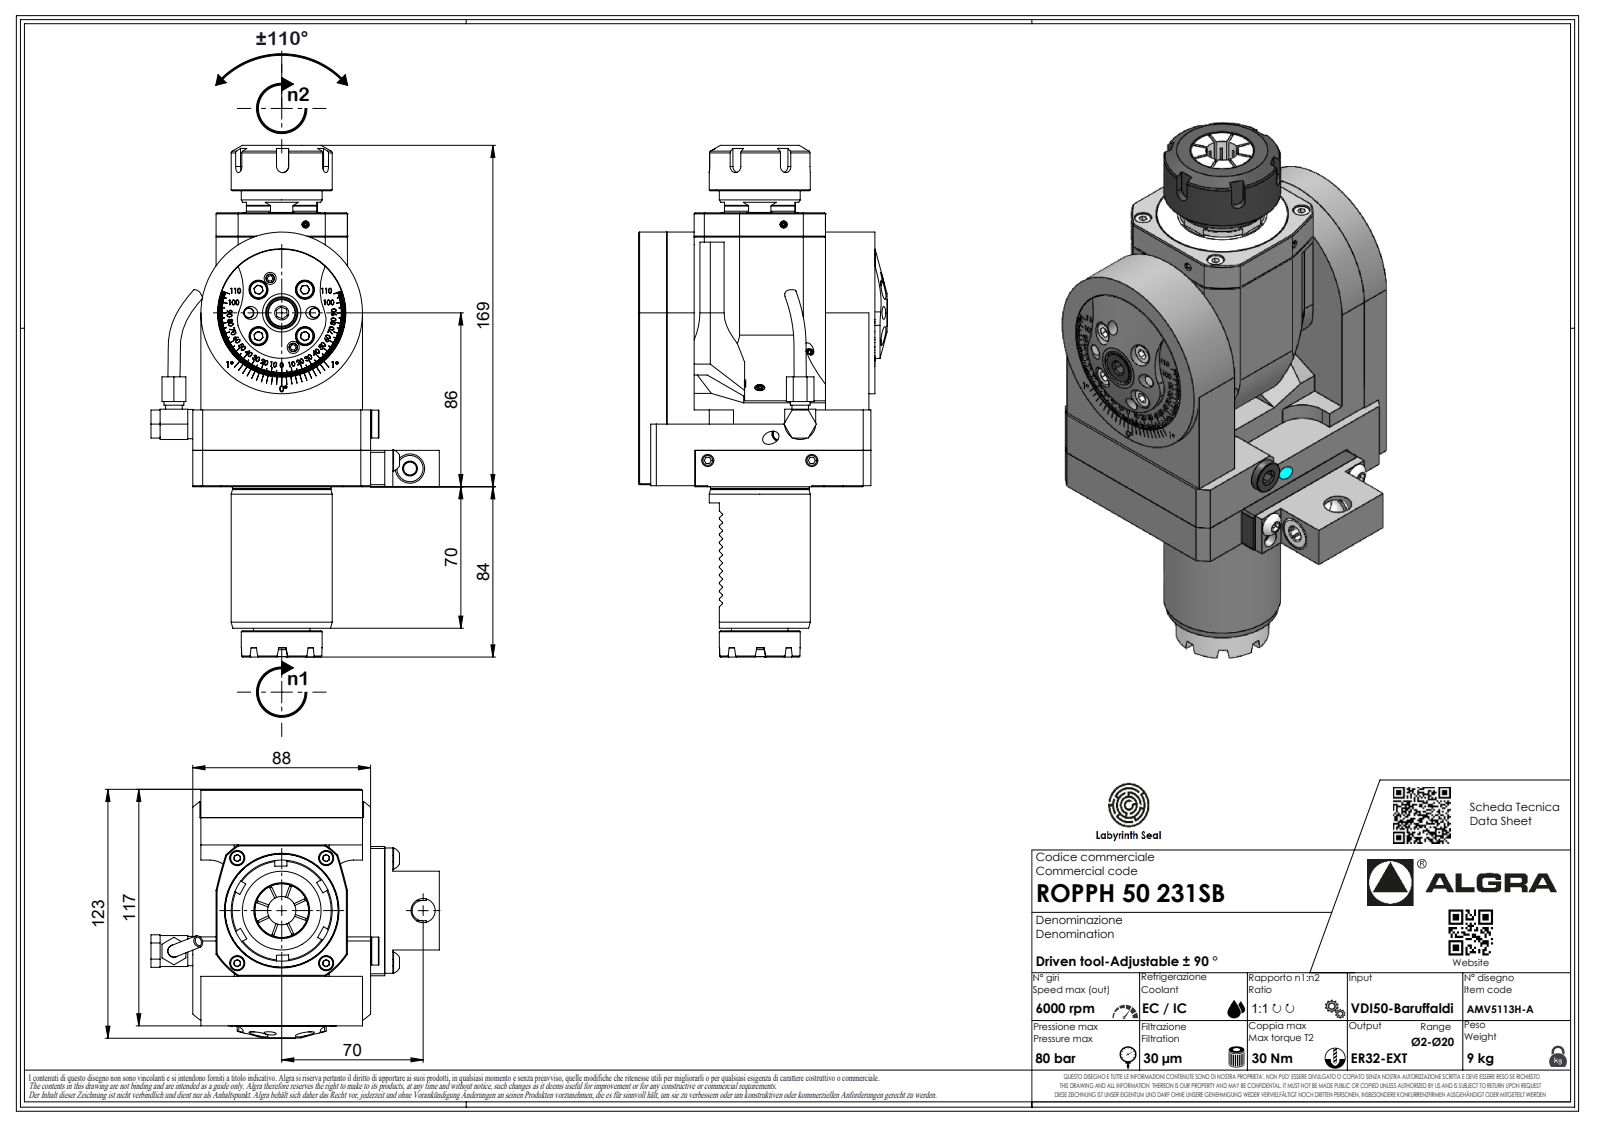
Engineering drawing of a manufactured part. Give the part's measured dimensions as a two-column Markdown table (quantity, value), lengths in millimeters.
| quantity | value |
| --- | --- |
| part name | ROPPH50231SB |
| STEP written by | SolidWorks 2023 (AUTOMOTIVE_DESIGN) |
| units | millimeters |
| bodies | 1 solid, 681 faces (413 planar, 121 cylindrical, 147 other) |
| overall size | 253.16 × 142.7 × 123 |
| volume | 1 277 000 mm³ |
| surface area | 113 349 mm² |
| round holes (diameter × count) | 2.1 × 1 |
| round bosses / shafts (diameter × count) | 80 × 1, 50 × 1, 48.7 × 1, 40 × 1, 28 × 1, 20.3 × 1, 14.5 × 1, 9.8 × 1 |
| partial cylindrical surfaces (radius × count) | 0.2 × 16, 0.3 × 12, 0.33 × 7, 0.52 × 7, 3.7 × 7, 3 × 5, 1 × 4, 10 × 2 |
| main face-to-face distances | 4, 65, 84, 0.5, 76.5, 11.5, 27.5, 22.5, 7.5, 72.5 |
